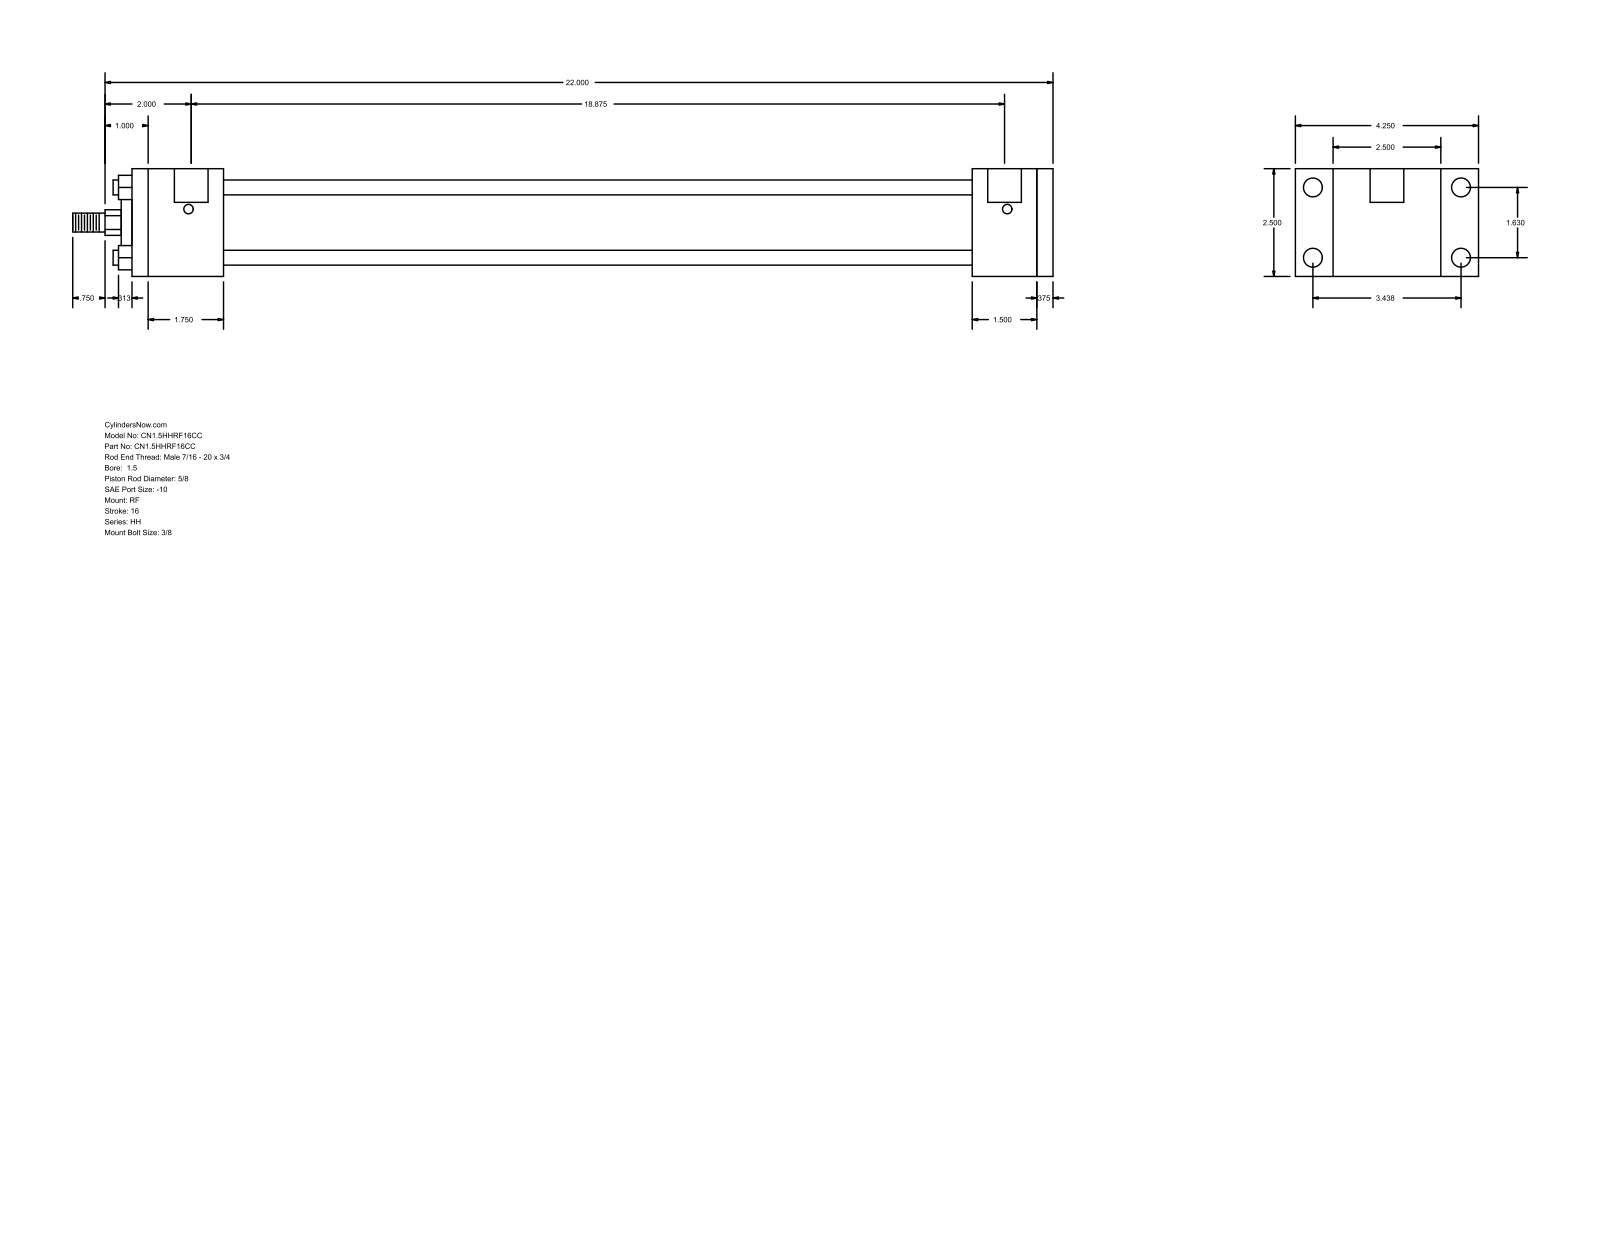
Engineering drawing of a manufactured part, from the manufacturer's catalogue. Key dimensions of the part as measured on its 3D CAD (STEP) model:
Part name (STEP PRODUCT): HH_RF__0150_0.625
STEP written by: GSSL Pune (CONFIG_CONTROL_DESIGN)
Units: millimetres
Bodies: 0 solids, 92 faces (64 planar, 28 cylindrical, 0 other)
Overall size (bounding box): 577.85 × 107.95 × 63.5
Round holes (diameter × count): ⌀5.56 ×4, ⌀11.13 ×4, ⌀19.84 ×2
Round bosses / shafts (diameter × count): ⌀8.76 ×4, ⌀44.45 ×1, ⌀28.57 ×1, ⌀15.88 ×1, ⌀11.11 ×1
Partial cylindrical surfaces — rounded edges, fillets, slot ends (radius × count): R7.54 ×1
Main face-to-face distances: 63.5, 542.92, 9.53, 533.39, 53.97, 495.3, 441.33, 479.42, 488.95, 38.09
Hole centre spacings: 41.4, 87.32, 96.64, 482.6, 1.58, 1.59, 479.43, 481.01
